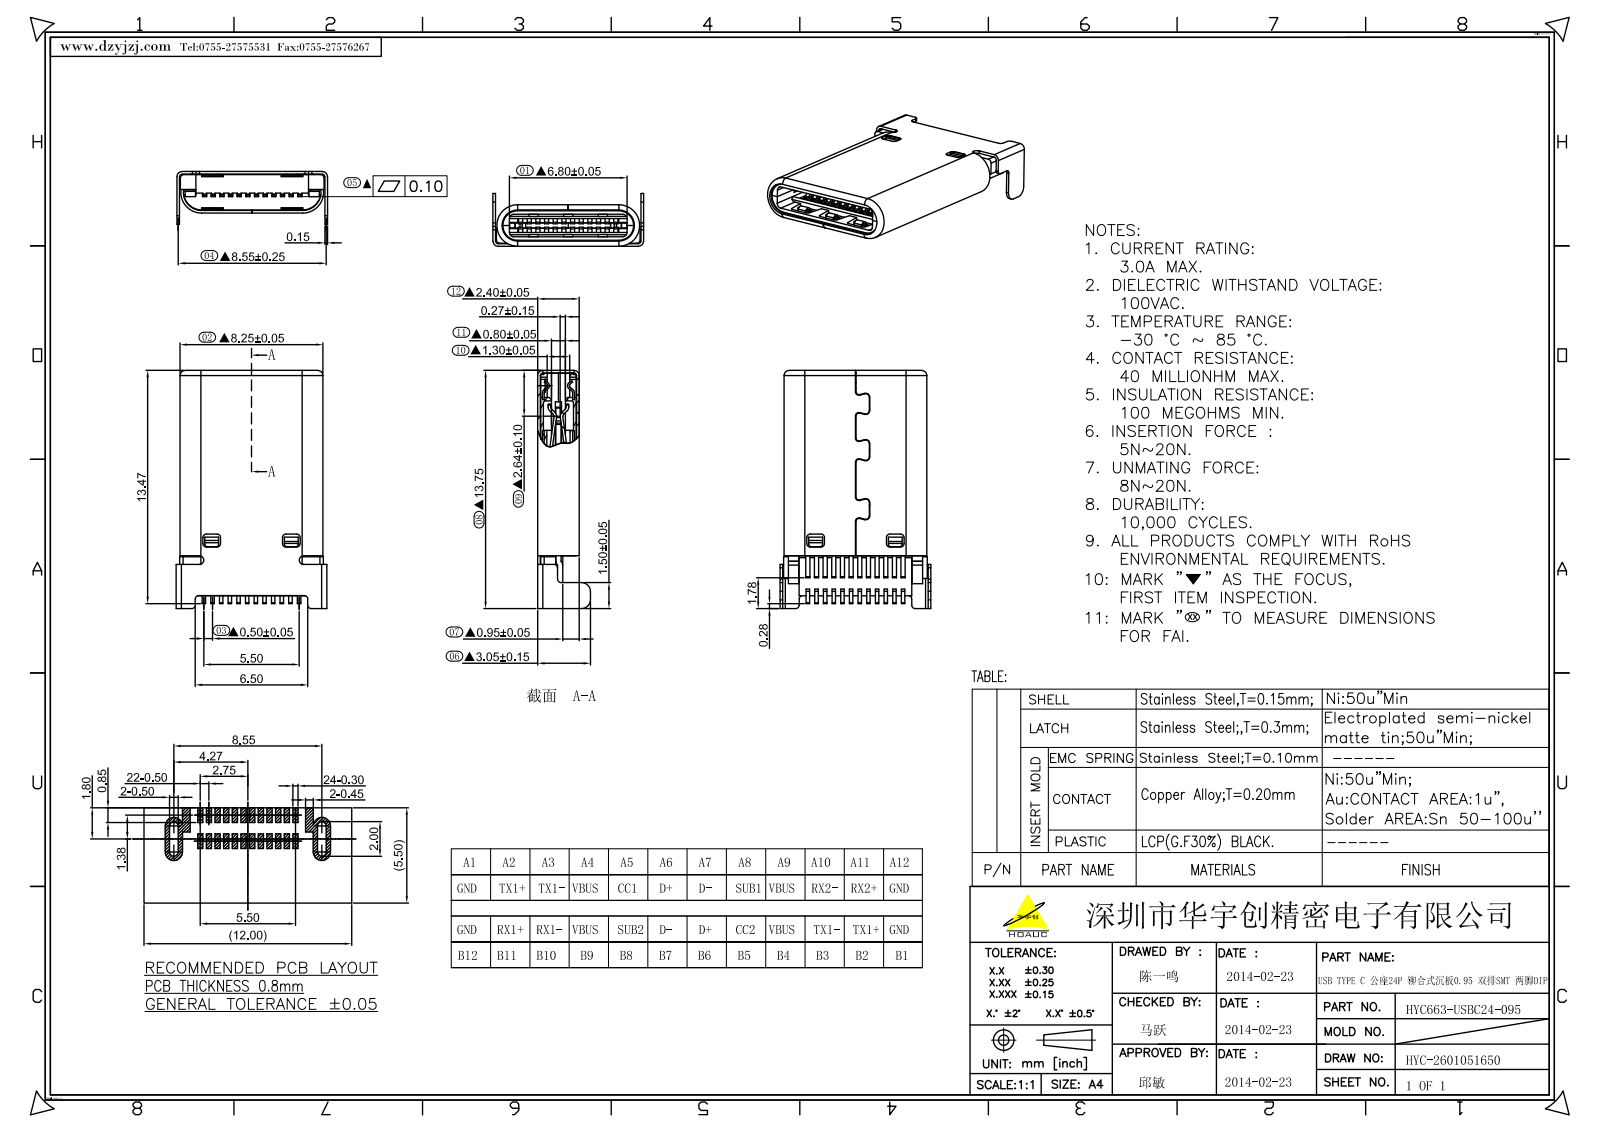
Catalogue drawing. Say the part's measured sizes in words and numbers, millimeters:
The part is named "TANPIAN-PLASTIC_1_2__2_1_3_1". Its 3-D file was written by "CREO PARAMETRIC BY PTC INC, 2022073 (CONFIG_CONTROL_DESIGN)". It is 1 solid with 739 faces: 559 planar, 176 cylindrical and 4 other. Overall it measures 13.75 by 8.7 by 3.05 millimeters. Its volume is 188 cubic millimeters and its surface area 498 square millimeters. Partial cylindrical surfaces (rounded edges, fillets, slot ends): 28 of radius 0.2, 12 of radius 0.25, 11 of radius 0.15, 8 of radius 0.3, 6 of radius 0.17, 6 of radius 0.23, 4 of radius 0.1, 4 of radius 0.13. The main face-to-face distances are 0.8, 2.4, 1.6, 0.65, 1.3, 1.45, 1.15, 0.95, 0.55, 1.05.
